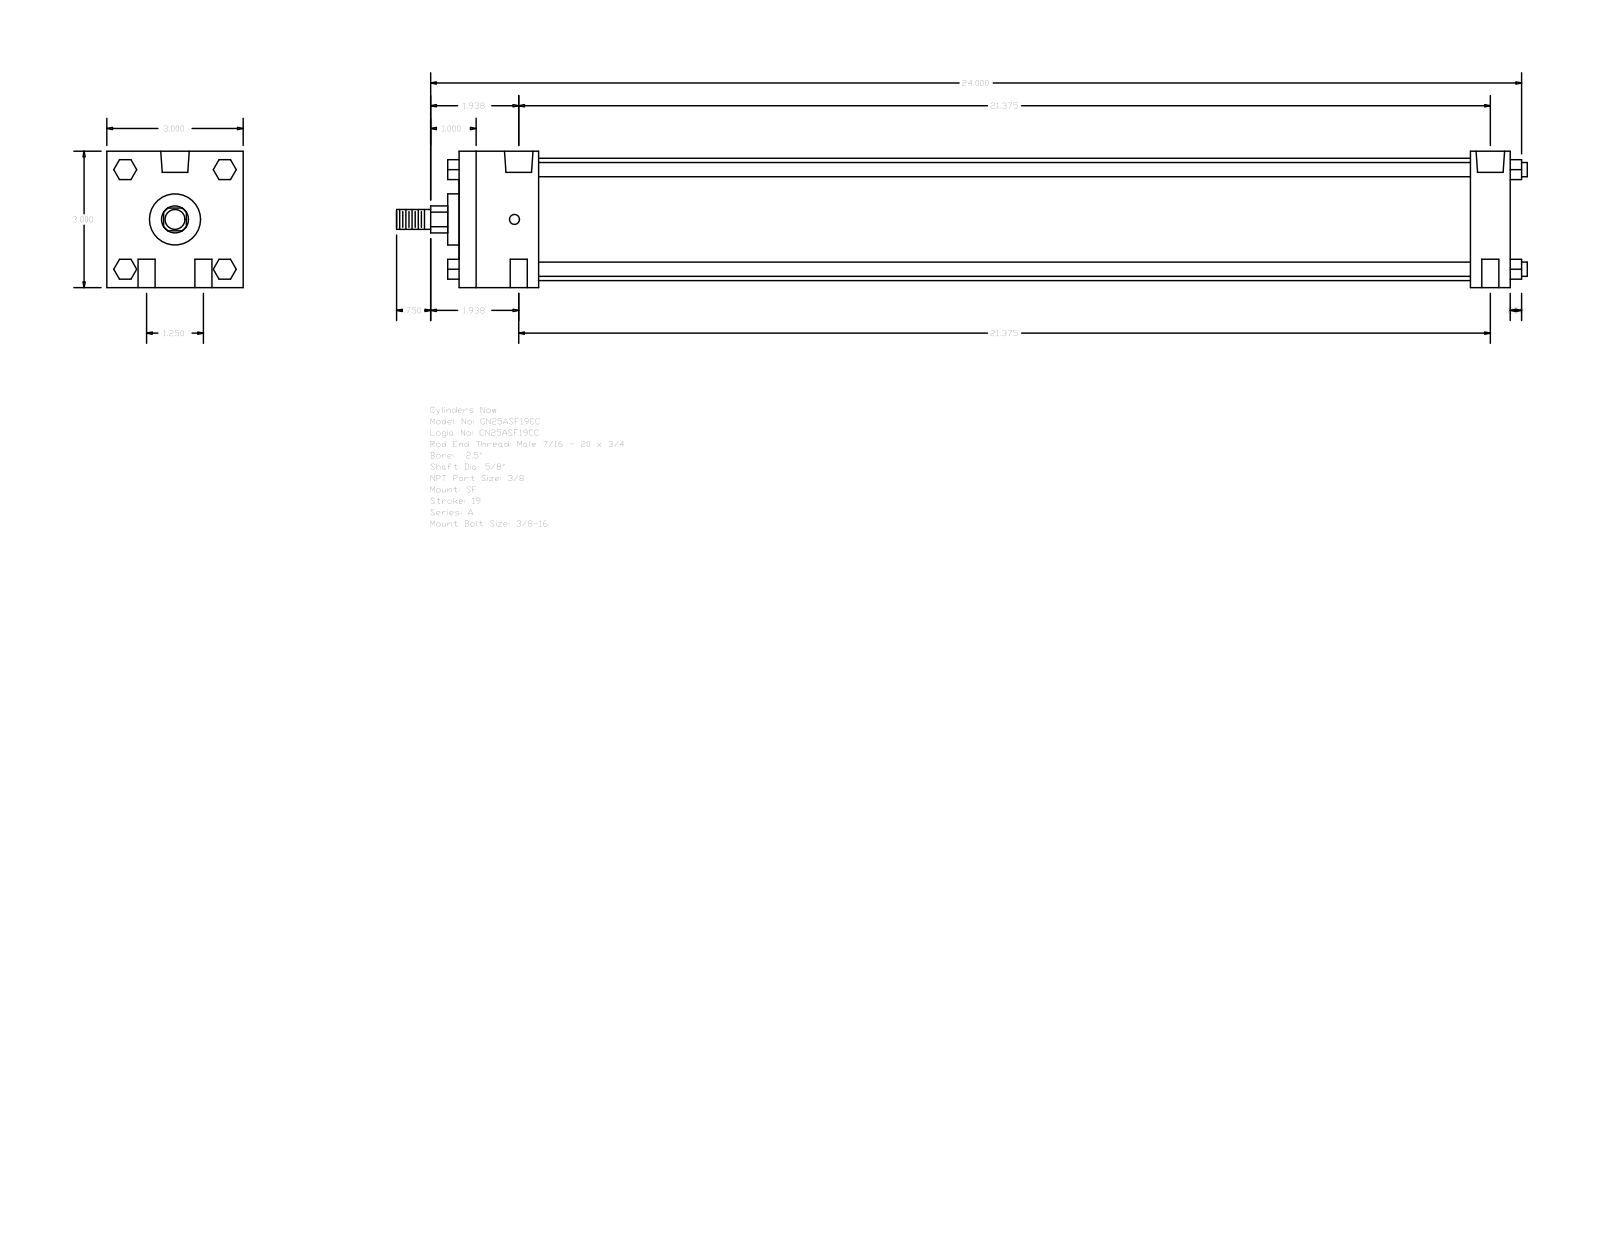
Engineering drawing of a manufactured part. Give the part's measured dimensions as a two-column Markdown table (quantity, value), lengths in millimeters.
| quantity | value |
| --- | --- |
| part name | A_SF__0250_0.625 |
| STEP written by | GSSL Pune (CONFIG_CONTROL_DESIGN) |
| units | millimeters |
| bodies | 0 solids, 124 faces (94 planar, 30 cylindrical, 0 other) |
| overall size | 631.83 × 76.2 × 76.2 |
| round holes (diameter × count) | 9.53 × 4, 5.56 × 2, 15.93 × 2 |
| round bosses / shafts (diameter × count) | 7.94 × 4, 68.33 × 1, 28.57 × 1, 15.88 × 1, 11.11 × 1 |
| partial cylindrical surfaces (radius × count) | 7.54 × 1 |
| main face-to-face distances | 76.2, 587.37, 44.45, 565.14, 22.23, 520.69, 542.92, 6.35, 593.72, 50.8 |
| hole center spacings | 15.88, 543.16, 542.93, 31.76, 543.86, 547.69 |
